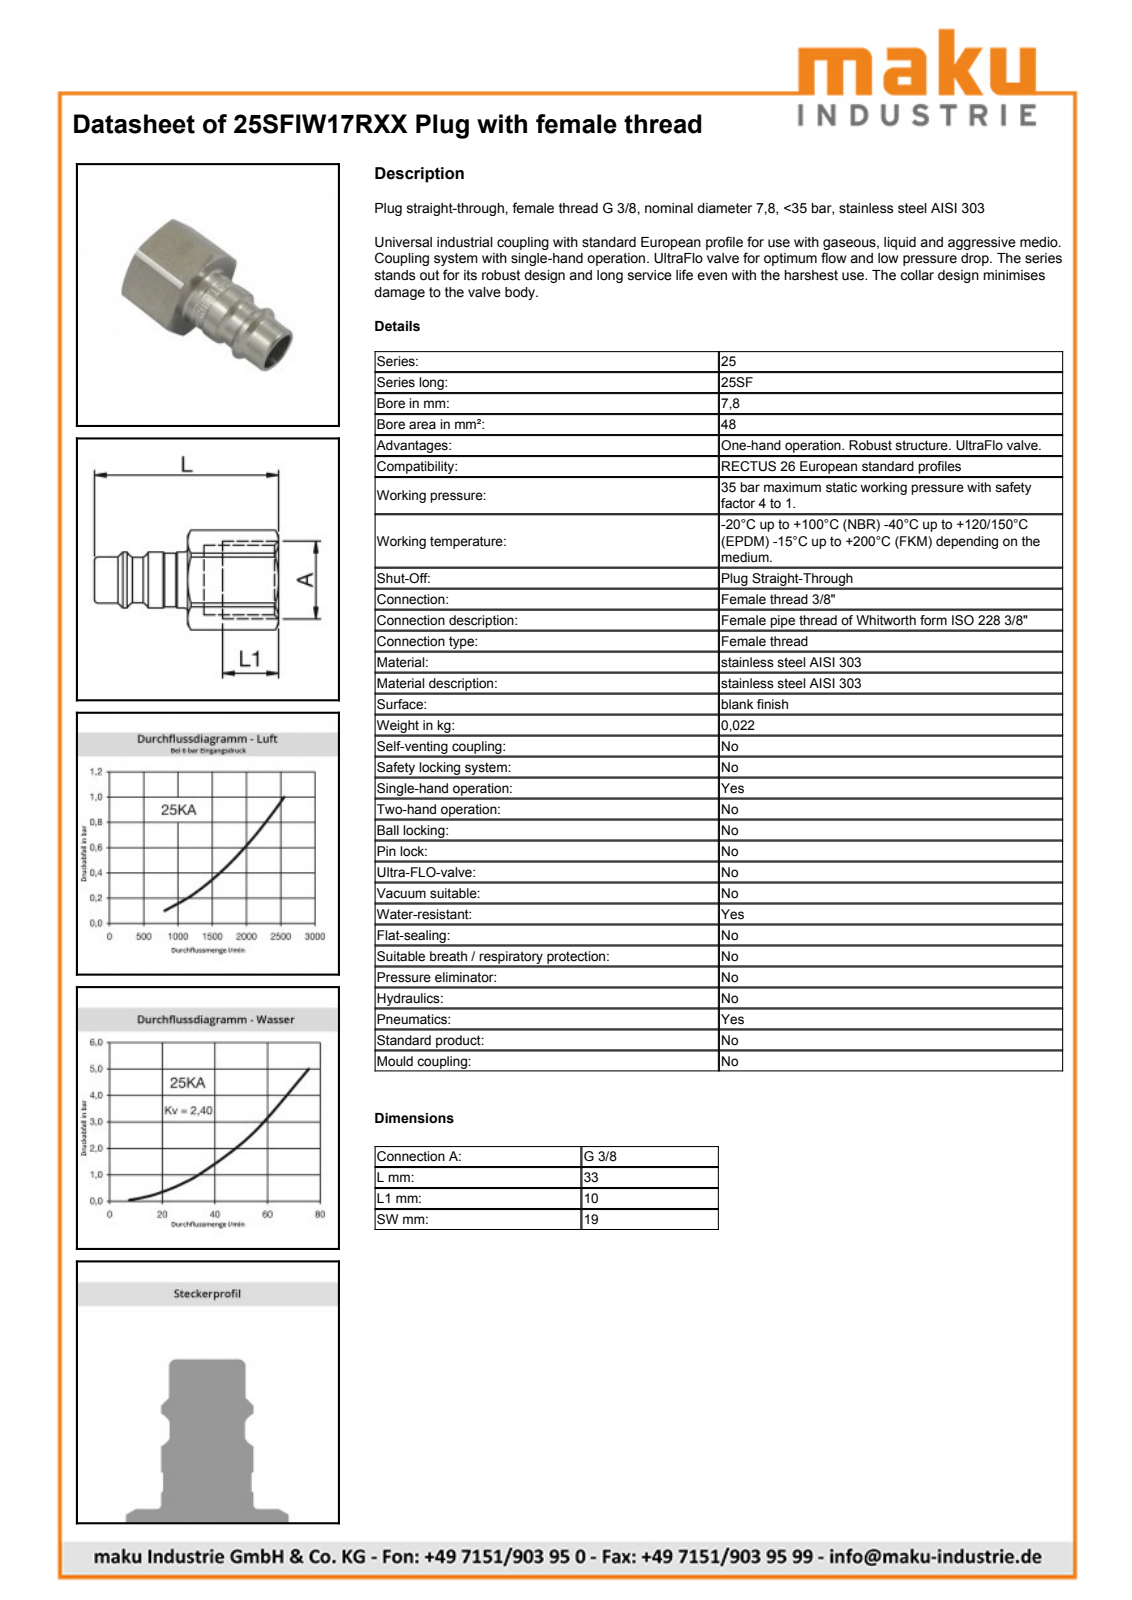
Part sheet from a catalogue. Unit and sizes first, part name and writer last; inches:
Units: inches
Overall size (bounding box): 1.299 × 0.843 × 0.748
Round holes (diameter × count): ⌀0.309 ×1, ⌀0.656 ×1
Round bosses / shafts (diameter × count): ⌀0.472 ×1, ⌀0.39 ×1, ⌀0.384 ×1
Partial cylindrical surfaces — rounded edges, fillets, slot ends (radius × count): R0.421 ×1
Main face-to-face distances: 0.748, 0.118, 0.512, 0.394, 0.787, 0.906, 1.299
Volume: 0.162 in³ · Surface area: 4.81 in²
Bodies: 1 solid, 40 faces (10 planar, 12 cylindrical, 18 other)
Part name (STEP PRODUCT): D108221
STEP written by: Autodesk Inventor 2013 (AUTOMOTIVE_DESIGN)
